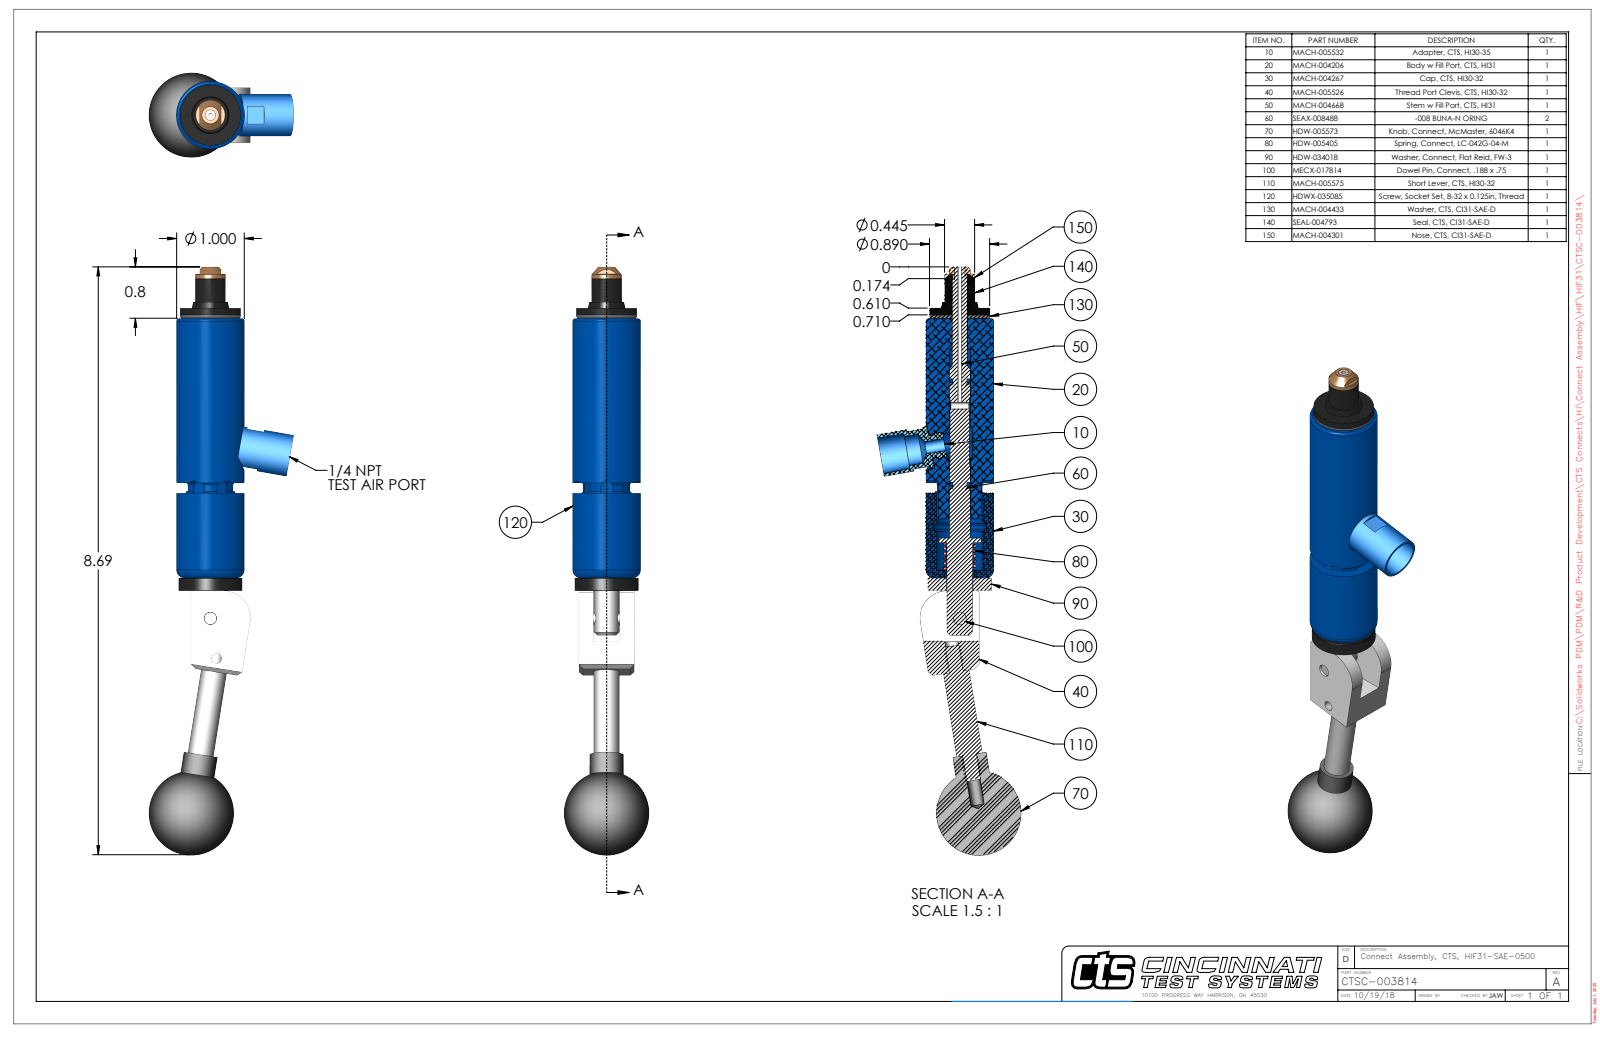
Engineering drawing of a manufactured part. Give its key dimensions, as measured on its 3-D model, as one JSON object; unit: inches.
{"part_name": "CTSC-003814", "step_written_by": "SolidWorks 2023 (AUTOMOTIVE_DESIGN)", "units": "inches", "bodies": {"solids": 9, "faces": 311, "planar": 116, "cylindrical": 124, "other": 71}, "overall_size": [8.692, 2.128, 1.25], "volume_in3": 5.135, "surface_area_in2": 40.39, "round_holes": [[0.15, 2], [0.201, 2], [0.063, 1], [0.109, 1], [0.136, 1], [0.187, 1], [0.189, 1], [0.228, 1], [0.229, 1], [0.385, 1], [0.392, 1], [0.438, 1]], "round_bosses_or_shafts": [[1, 1], [0.936, 1], [0.89, 1], [0.62, 1], [0.5, 1], [0.445, 1], [0.445, 1], [0.38, 1]], "partial_cylinders_radius": [[0.093, 6], [0.029, 2], [0.062, 1], [0.325, 1], [0.375, 1], [0.4, 1], [0.458, 1]], "face_to_face_distances": [0.21, 0.602, 0.05, 3.885, 3.835, 0.812, 4.072, 4.022, 0.187, 0.391], "hole_center_spacings": [0.599, 1.658, 2.252]}
